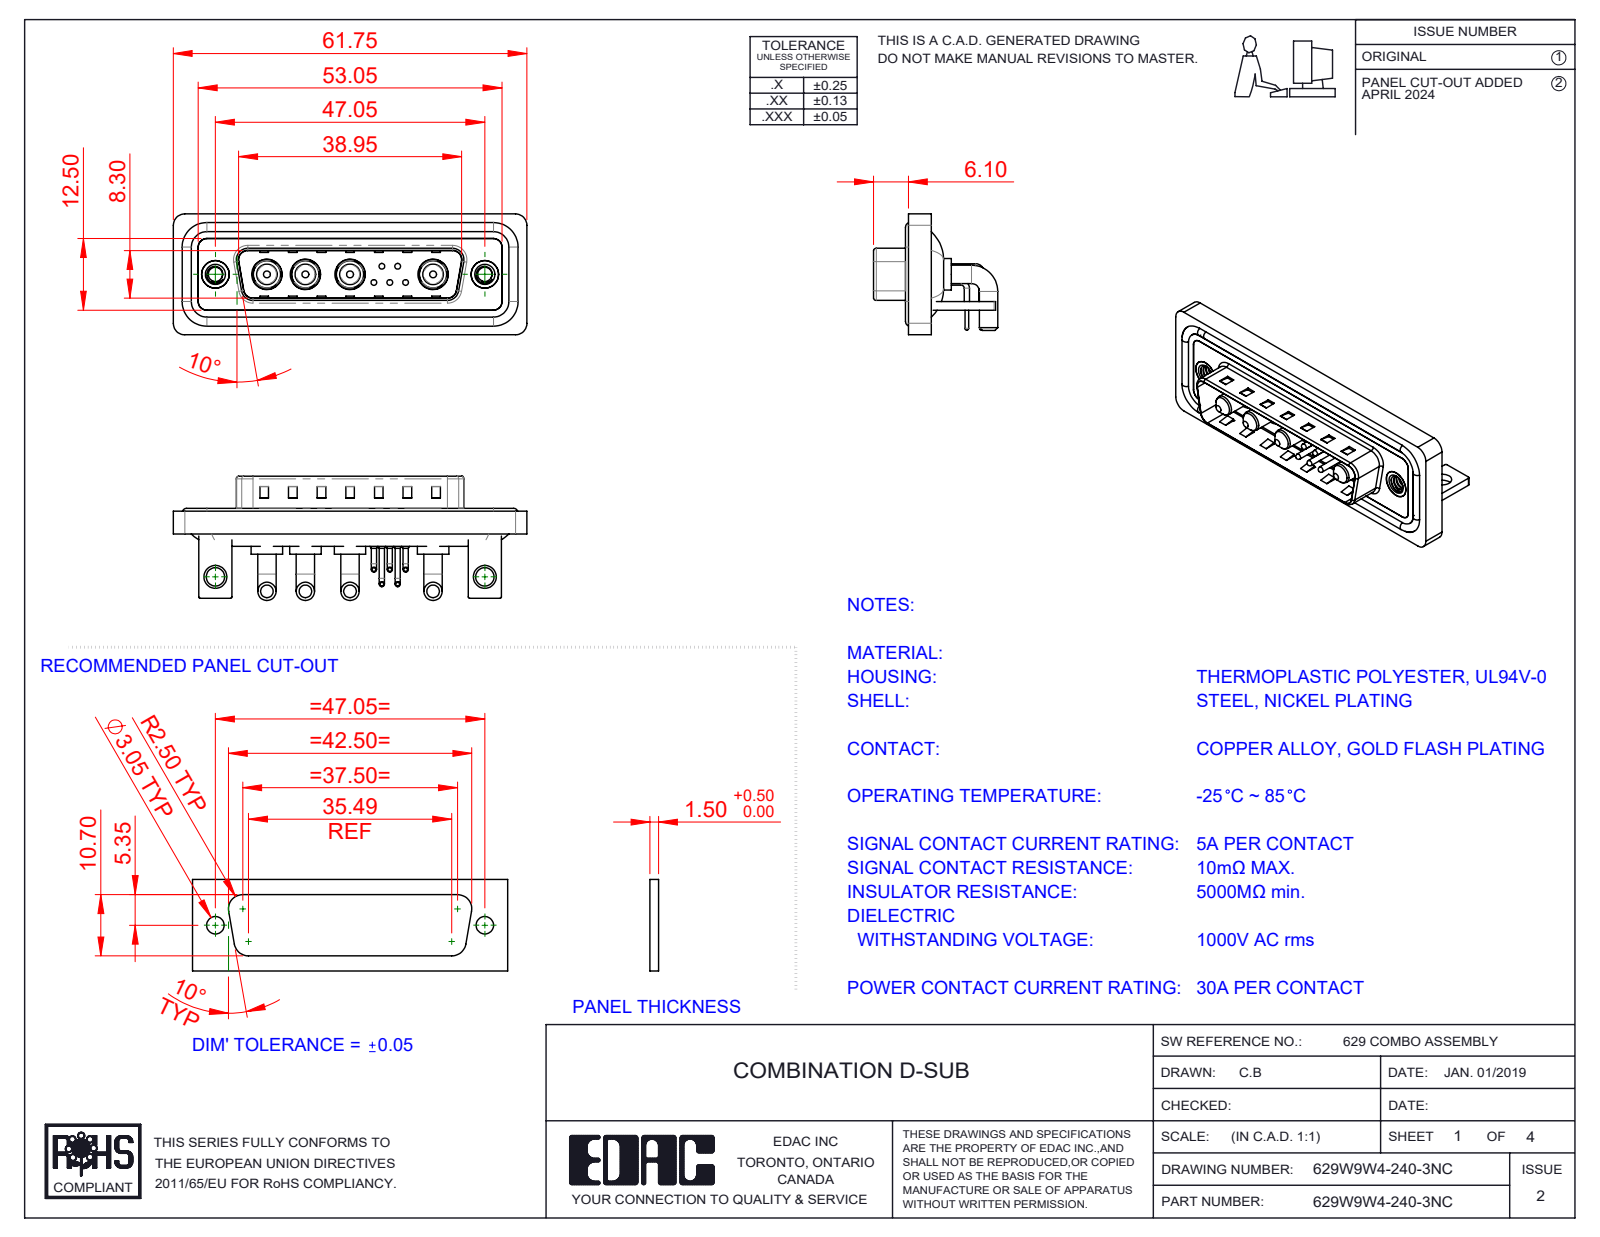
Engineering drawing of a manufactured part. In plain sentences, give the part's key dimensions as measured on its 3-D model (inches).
The part is named "629Combo Stabilizer Bracket; 629Combo Waterproof Housing_25 Contacts; Power Pin_30A RA; 629Combo Shell Rear_25 Contacts (+6 more)". Its 3-D file was written by "SolidWorks 2023 (CONFIG_CONTROL_DESIGN)". It is 22 solids with 1243 faces: 589 planar, 470 cylindrical and 184 other. Overall it measures 2.431 by 0.854 by 0.831 inches. Its volume is 0.494 cubic inches and its surface area 20.21 square inches. Round holes: 5 of diameter 0.03, 5 of diameter 0.063, 5 of diameter 0.079, 4 of diameter 0.191, 4 of diameter 0.209, 2 of diameter 0.098, 2 of diameter 0.126, 2 of diameter 0.157, 2 of diameter 0.189, 2 of diameter 0.197. Round bosses or shafts: 10 of diameter 0.035, 8 of diameter 0.126, 5 of diameter 0.059, 5 of diameter 0.039, 5 of diameter 0.026, 4 of diameter 0.217, 4 of diameter 0.205, 4 of diameter 0.187. Partial cylindrical surfaces (rounded edges, fillets, slot ends): 19 of radius 0.079, 18 of radius 0.059, 16 of radius 0.01, 9 of radius 0.02, 8 of radius 0.063, 5 of radius 0.04, 4 of radius 0.024, 4 of radius 0.026. The main face-to-face distances are 0.016, 0.059, 0.031, 0.114, 0.083, 0.043, 0.146, 0.161, 0.177, 0.063. The hole center spacings are 0.124, 0.109, 0.198, 0.571, 1.852, 0.109, 0.173, 0.174.
